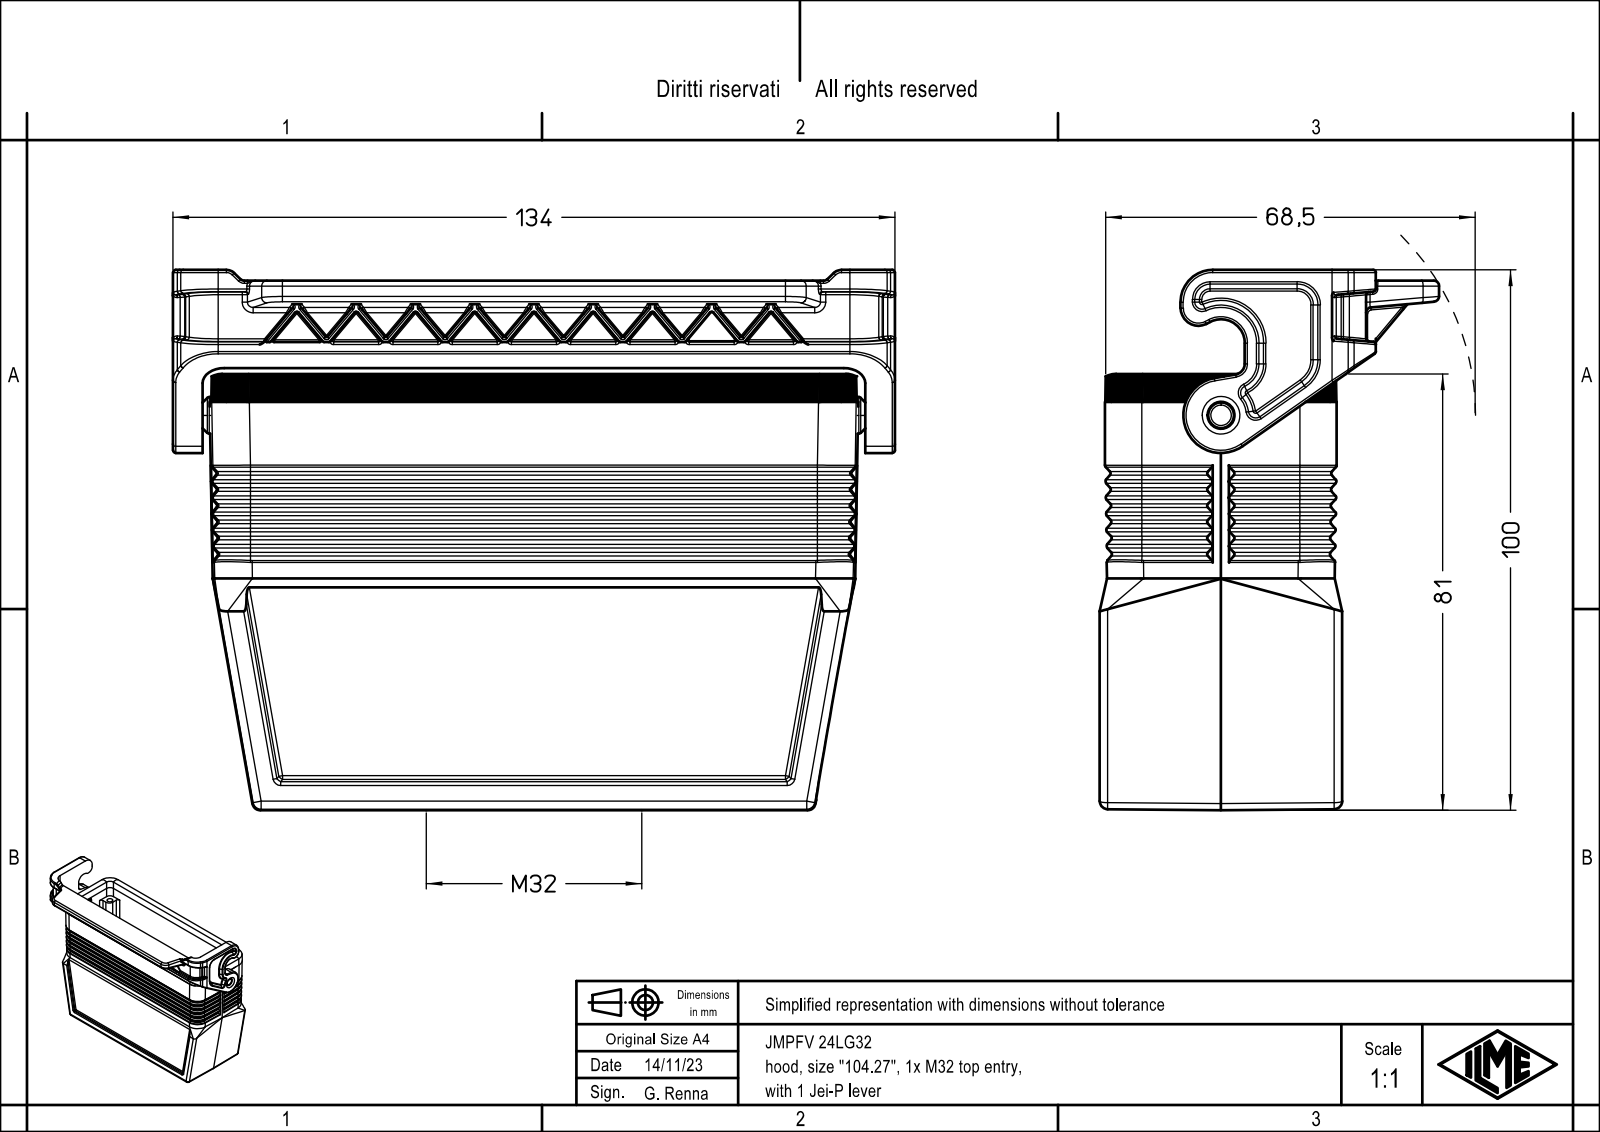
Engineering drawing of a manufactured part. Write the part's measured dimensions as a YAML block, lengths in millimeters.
part_name: "JMPFV 24LG32"
step_written_by: "Creo Elements/Direct Modeling 20.1B 02-Apr-2019 (C) Parametric Technology GmbH (AUTOMOTIVE_DESIGN)"
units: millimeters
bodies: {solids: 1, faces: 1242, planar: 358, cylindrical: 465, other: 419}
overall_size: [134, 100.25, 63]
volume: 131142
surface_area: 69778
round_holes:
  - {diameter: 3, count: 4}
  - {diameter: 3.5, count: 4}
  - {diameter: 4.8, count: 1}
  - {diameter: 30.6, count: 1}
round_bosses_or_shafts:
  - {diameter: 6.8, count: 1}
partial_cylinders:
  - {radius: 0.5, count: 147}
  - {radius: 0.3, count: 126}
  - {radius: 1, count: 27}
  - {radius: 1.5, count: 22}
  - {radius: 0.33, count: 15}
  - {radius: 7, count: 13}
  - {radius: 3, count: 12}
  - {radius: 4, count: 8}
face_to_face_distances: [3.75, 39.25, 35.5, 43, 2, 7, 4, 3.25, 42.5, 46.25]
hole_center_spacings: [53.72, 27, 104, 107.45]
